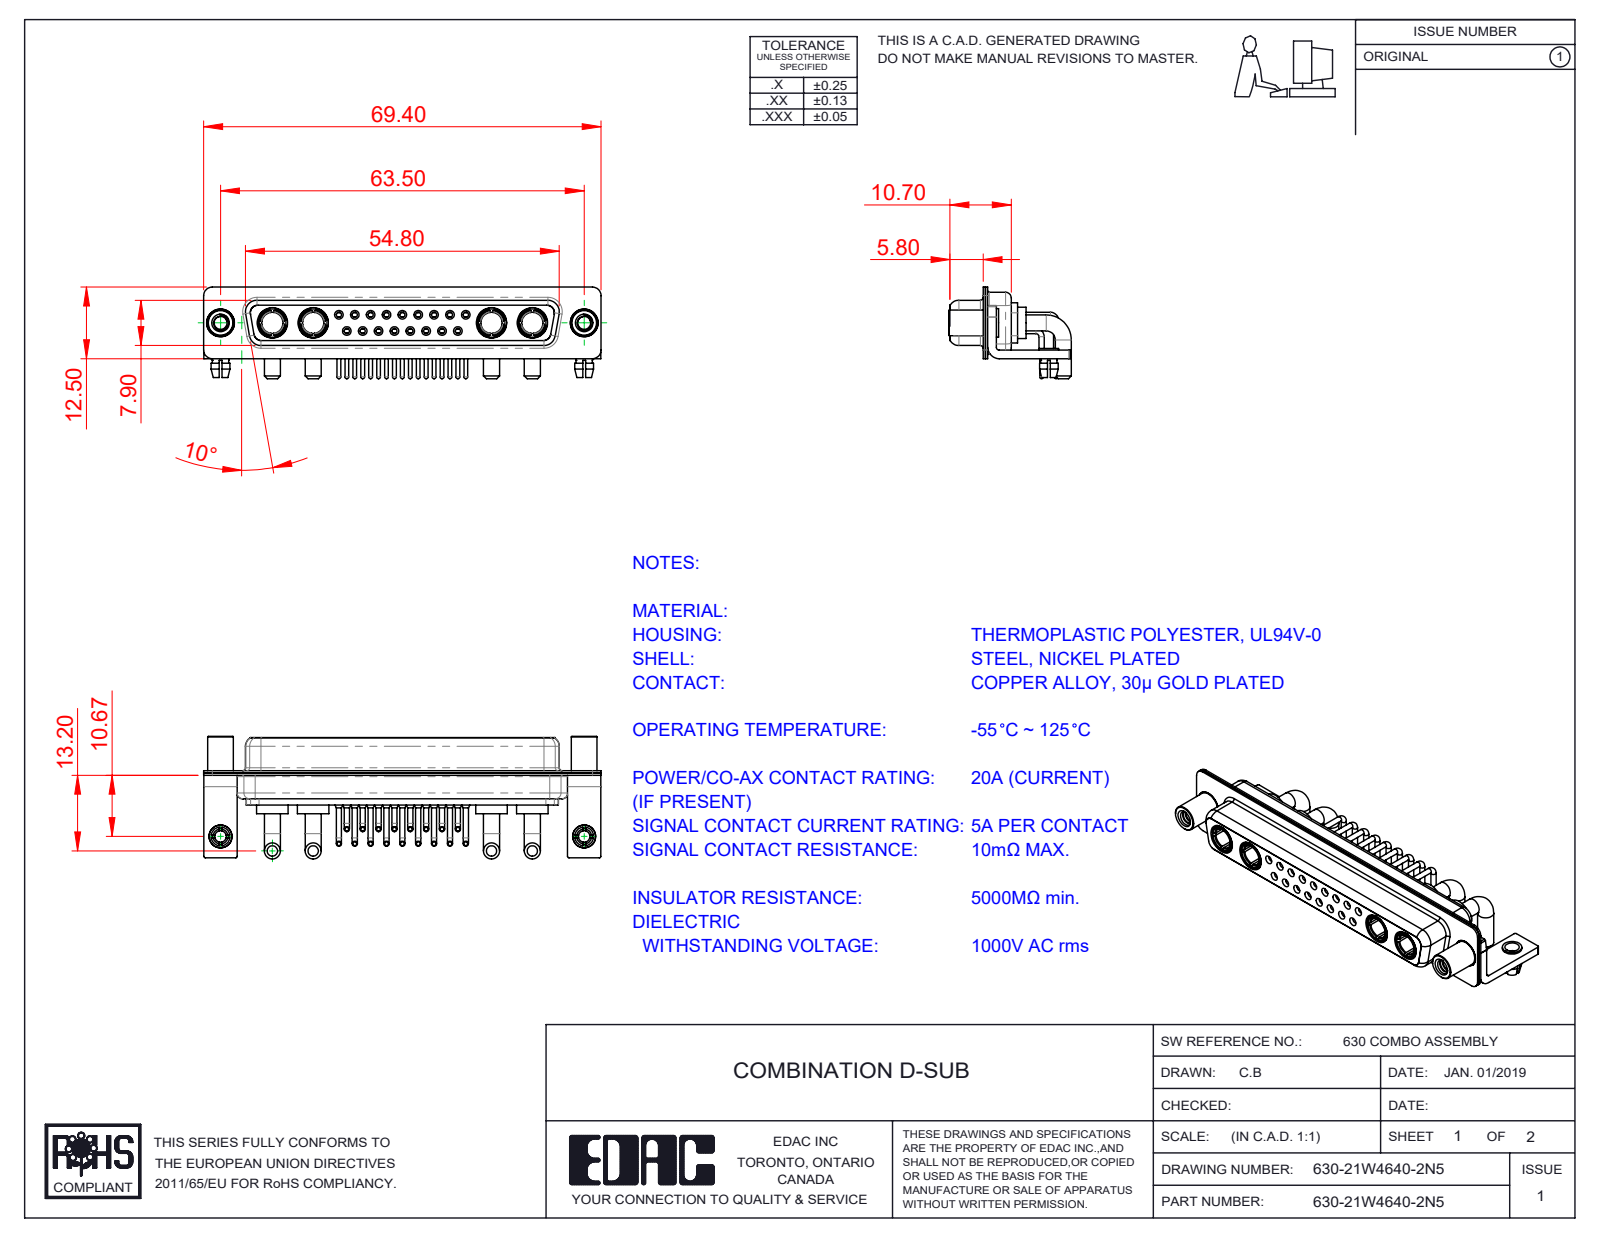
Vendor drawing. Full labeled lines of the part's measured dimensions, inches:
Part name (STEP PRODUCT): 630Combo Contact Row 2; 630Combo Contact Row 1; 630Combo Housing_21W4; 630-21W4640-2N5 (+6 more)
STEP written by: SolidWorks 2020 (CONFIG_CONTROL_DESIGN)
Units: inches
Bodies: 34 solids, 1672 faces (508 planar, 720 cylindrical, 444 other)
Overall size (bounding box): 2.732 × 0.843 × 0.63
Volume: 0.373 in³ · Surface area: 21.21 in²
Round holes (diameter × count): ⌀0.079 ×19, ⌀0.035 ×17, ⌀0.043 ×17, ⌀0.059 ×17, ⌀0.067 ×9, ⌀0.063 ×8, ⌀0.191 ×6, ⌀0.146 ×4, ⌀0.209 ×4, ⌀0.089 ×2, ⌀0.098 ×2, ⌀0.126 ×2
Round bosses / shafts (diameter × count): ⌀0.035 ×23, ⌀0.026 ×17, ⌀0.063 ×15, ⌀0.11 ×8, ⌀0.079 ×6, ⌀0.059 ×6, ⌀0.217 ×4, ⌀0.205 ×4
Partial cylindrical surfaces — rounded edges, fillets, slot ends (radius × count): R0.01 ×16, R0.059 ×16, R0.079 ×13, R0.053 ×8, R0.063 ×8, R0.02 ×5, R0.024 ×4, R0.026 ×4
Main face-to-face distances: 0.016, 0.018, 0.055, 0.333, 0.071, 0.35, 0.244, 0.278, 0.031, 0.295
Hole centre spacings: 0.124, 0.109, 0.218, 0.327, 0.198, 0.198, 0.295, 0.436
